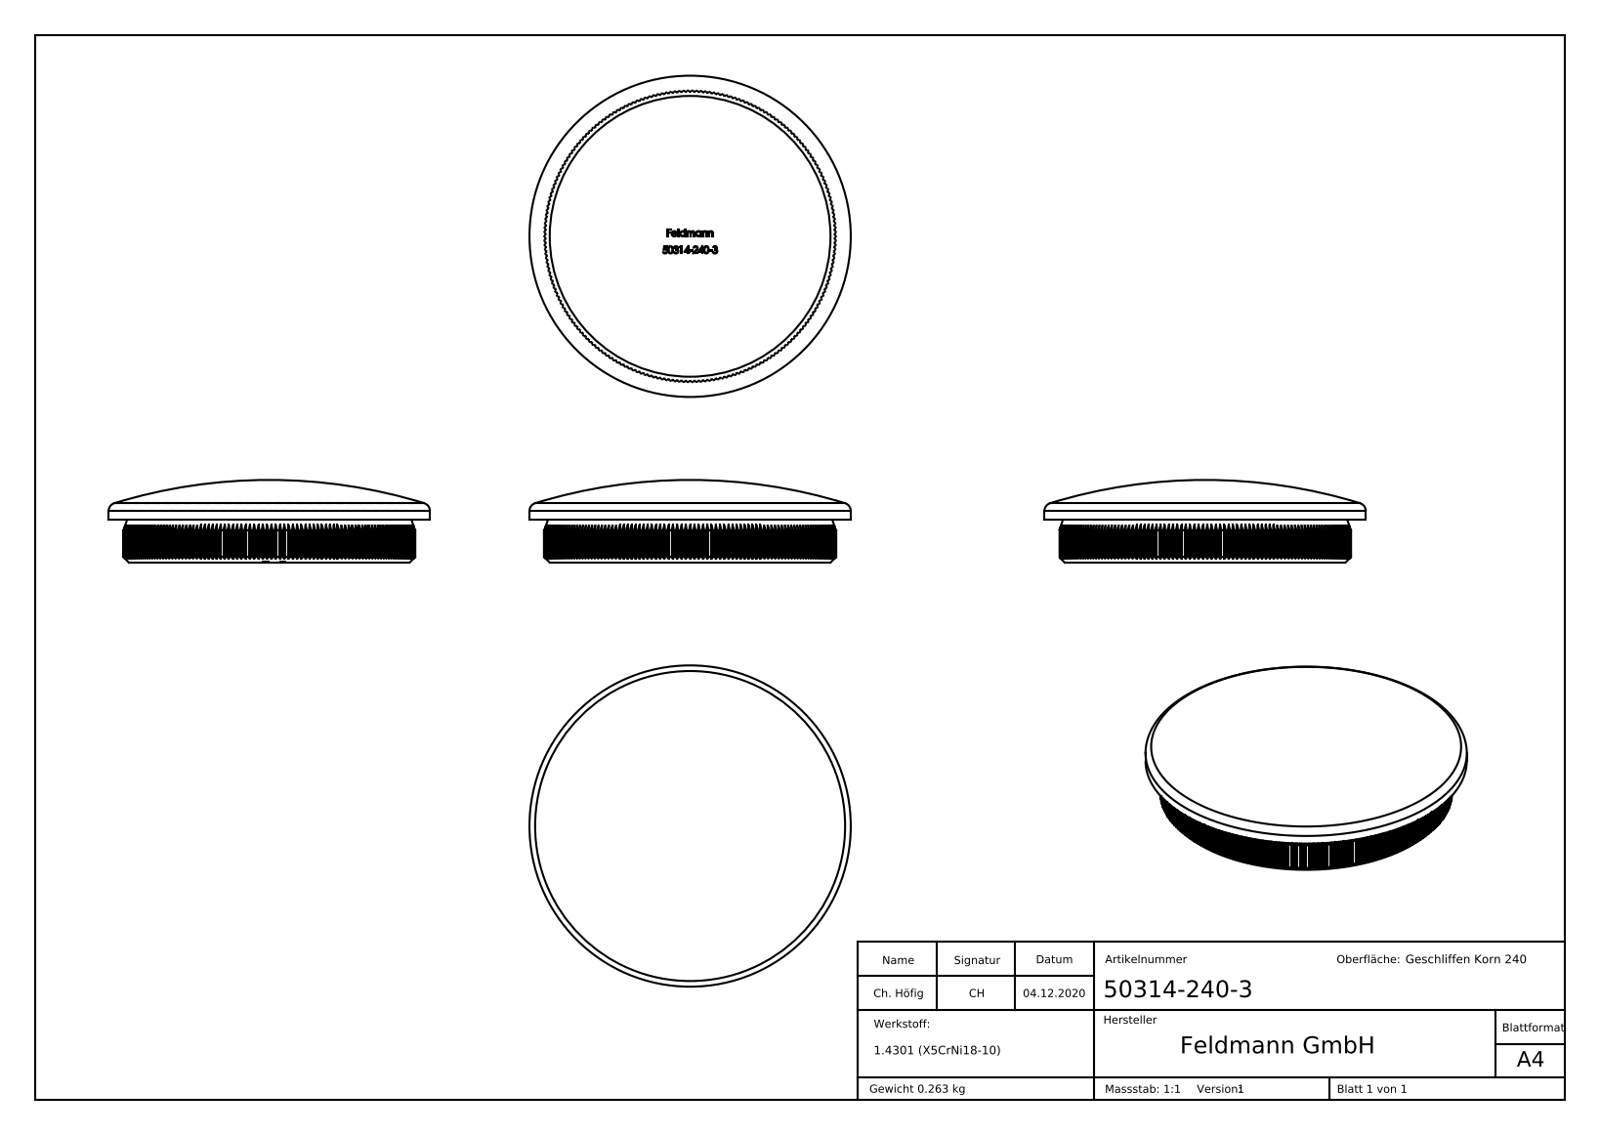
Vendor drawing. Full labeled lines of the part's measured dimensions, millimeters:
Part name (STEP PRODUCT): 50314-240-3
STEP written by: SolidWorks 2018 (CONFIG_CONTROL_DESIGN)
Units: millimetres
Bodies: 1 solid, 888 faces (560 planar, 212 cylindrical, 116 other)
Overall size (bounding box): 60.3 × 60.3 × 15.5
Volume: 33 241 mm³ · Surface area: 8 135 mm²
Round bosses / shafts (diameter × count): ⌀60.3 ×1
Partial cylindrical surfaces — rounded edges, fillets, slot ends (radius × count): R27.35 ×1
Main face-to-face distances: 8, 27, 26.99, 27.02, 26.98, 27.01, 7.9, 27.04, 0.58, 2.64
